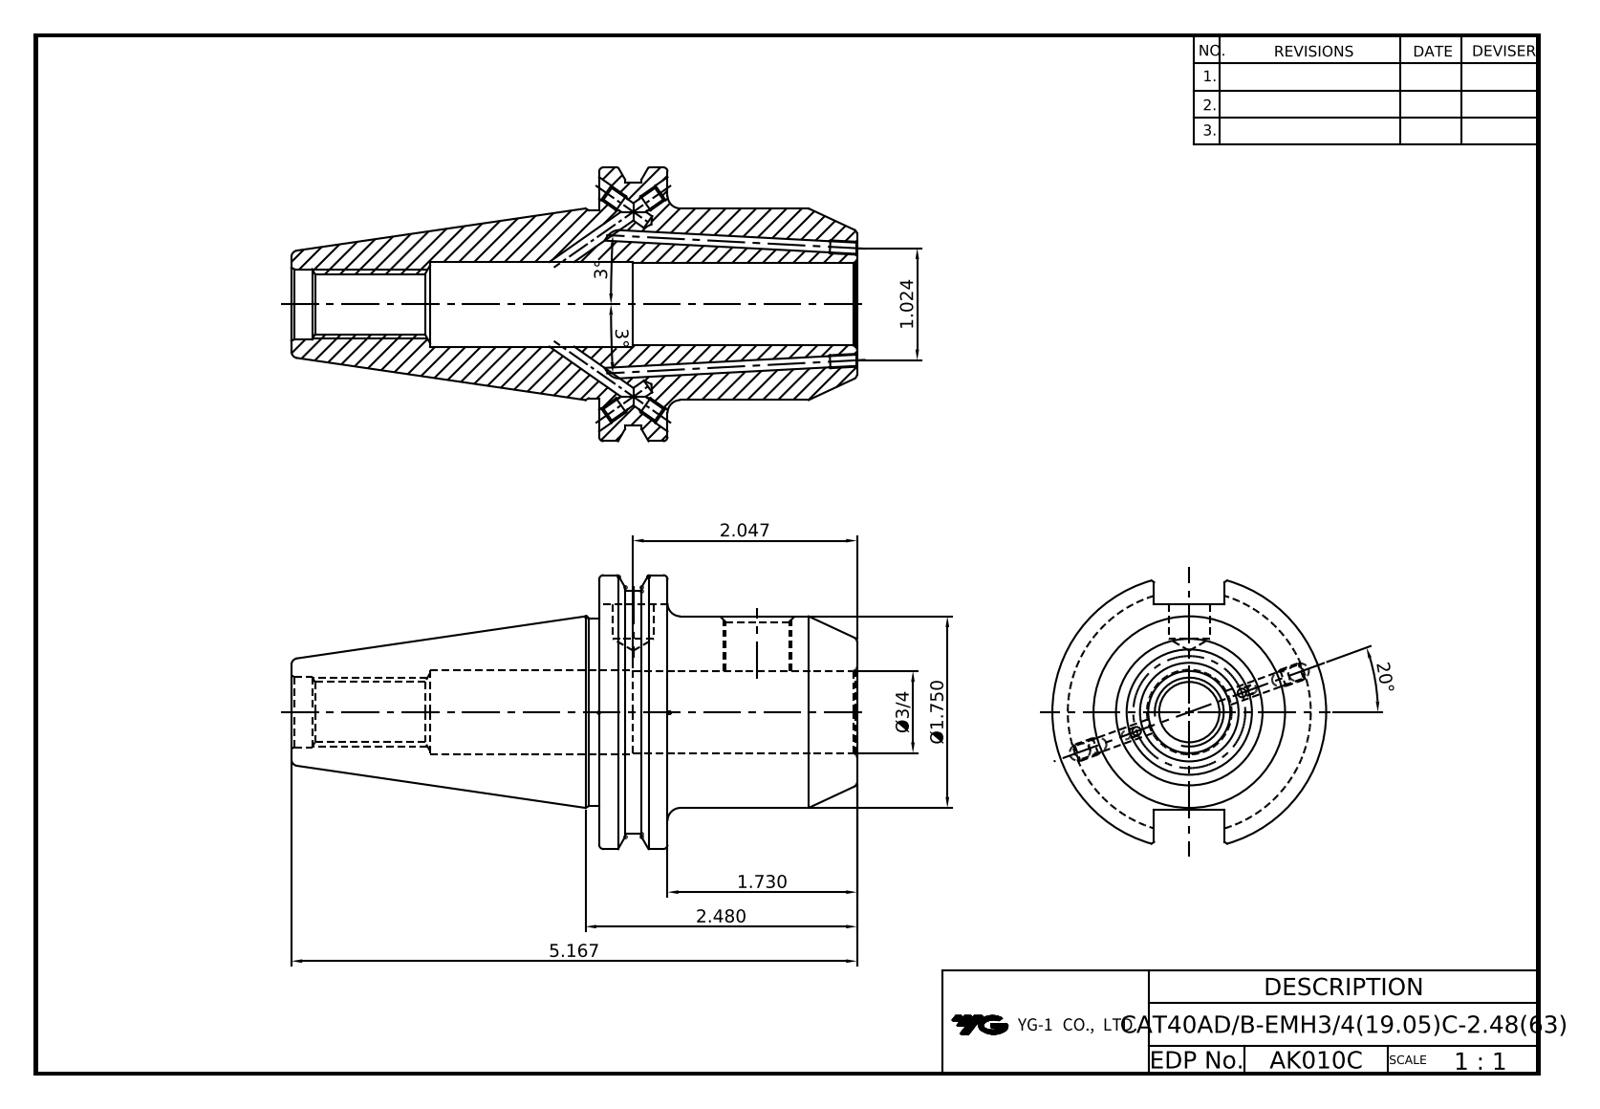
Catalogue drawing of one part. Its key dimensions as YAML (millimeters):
part_name: "CAT40ADB-EMH19_05C-63-PB15"
step_written_by: "CREO PARAMETRIC BY PTC INC, 2018400 (CONFIG_CONTROL_DESIGN)"
units: millimeters
bodies: {solids: 1, faces: 130, planar: 38, cylindrical: 50, other: 42}
overall_size: [131.25, 63.5, 61.09]
volume: 139526
surface_area: 31335
round_holes:
  - {diameter: 3.24, count: 4}
  - {diameter: 4, count: 4}
  - {diameter: 2.6, count: 2}
  - {diameter: 9.53, count: 1}
  - {diameter: 13.39, count: 1}
  - {diameter: 14.7, count: 1}
  - {diameter: 16.3, count: 1}
  - {diameter: 19.05, count: 1}
  - {diameter: 19.65, count: 1}
round_bosses_or_shafts:
  - {diameter: 63.5, count: 1}
  - {diameter: 56.3, count: 1}
  - {diameter: 44.45, count: 1}
  - {diameter: 43.6, count: 1}
face_to_face_distances: [15.88, 59.83, 43.95, 47.6, 39.23, 55.11, 99.06, 16.38, 32.19, 71.42]
hole_center_spacings: [35.13, 28.77]
